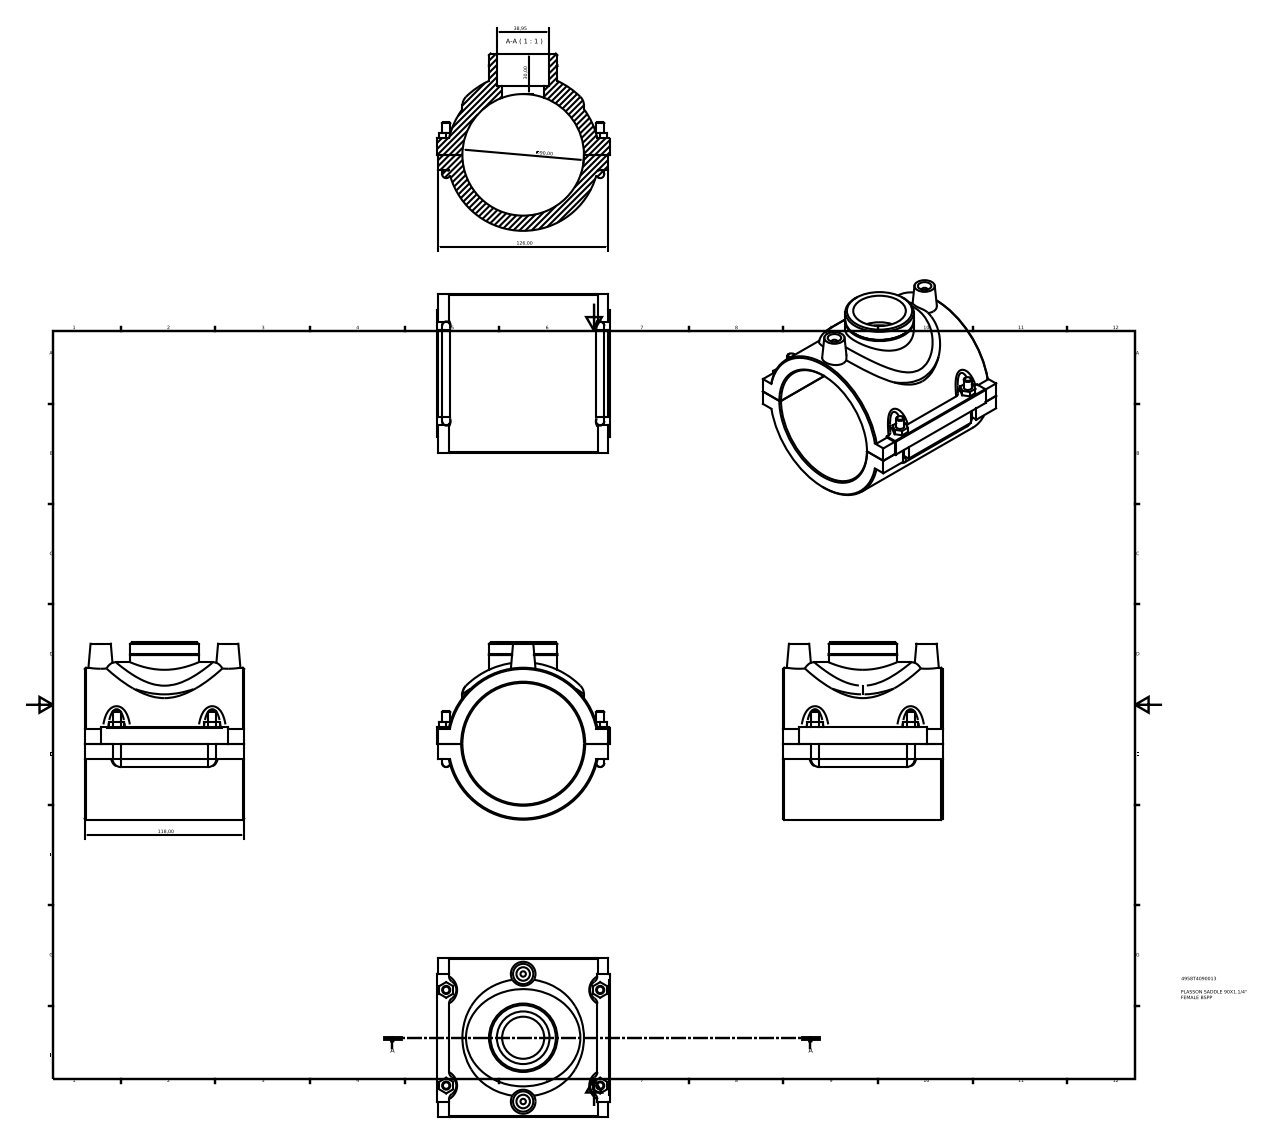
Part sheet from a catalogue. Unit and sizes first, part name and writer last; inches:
Units: inches
Overall size (bounding box): 5.167 × 5.039 × 4.646
Round holes (diameter × count): ⌀0.394 ×2, ⌀1.227 ×1, ⌀1.533 ×1, ⌀3.543 ×1
Round bosses / shafts (diameter × count): ⌀0.236 ×6, ⌀0.157 ×2, ⌀4.429 ×1, ⌀1.994 ×1, ⌀1.954 ×1
Partial cylindrical surfaces — rounded edges, fillets, slot ends (radius × count): R0.295 ×4, R0.02 ×1, R1.772 ×1, R2.374 ×1
Main face-to-face distances: 4.646, 0.039, 5, 0.441, 0.445, 0.925, 0.484, 0.48, 4.961, 5.039
Hole centre spacings: 1.858, 3.717
Volume: 30.32 in³ · Surface area: 165.4 in²
Bodies: 1 solid, 159 faces (86 planar, 39 cylindrical, 34 other)
Part name (STEP PRODUCT): 4958T4090013
STEP written by: Autodesk Inventor 2015 (AUTOMOTIVE_DESIGN)
